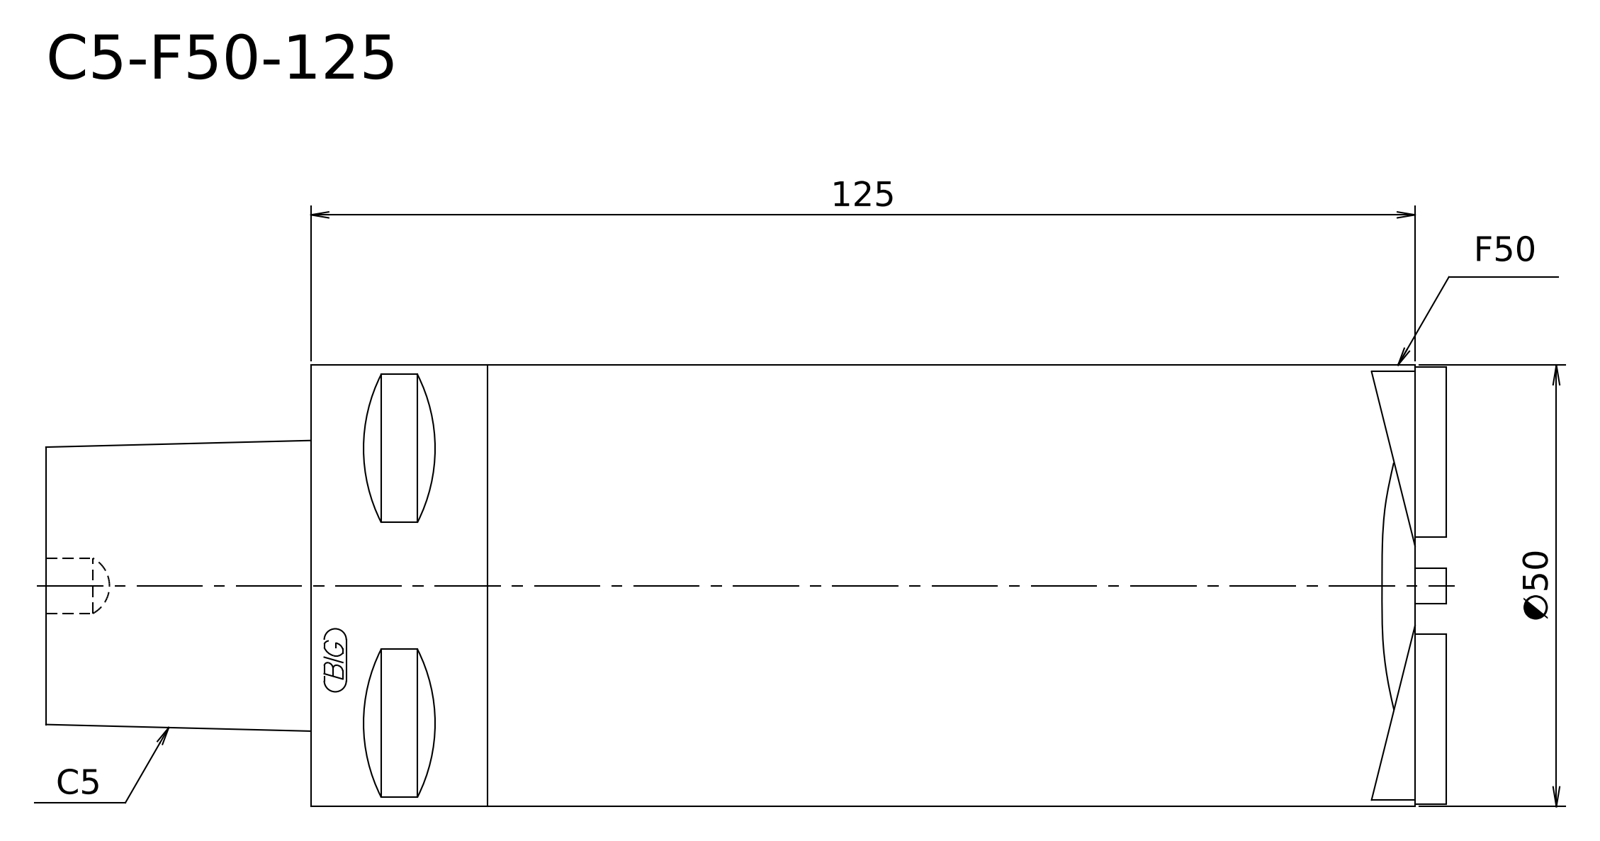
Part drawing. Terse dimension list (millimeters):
name: C5-F50-125
written by: SolidWorks 2021 (CONFIG_CONTROL_DESIGN)
unit: mm
bodies: 1 solid, 7 faces (3 planar, 2 cylindrical, 2 other)
size: 155 × 50 × 50
volume: 269 811 mm³; area: 26 518 mm²
bosses: 1× ⌀50
face distances: 125, 30, 155
